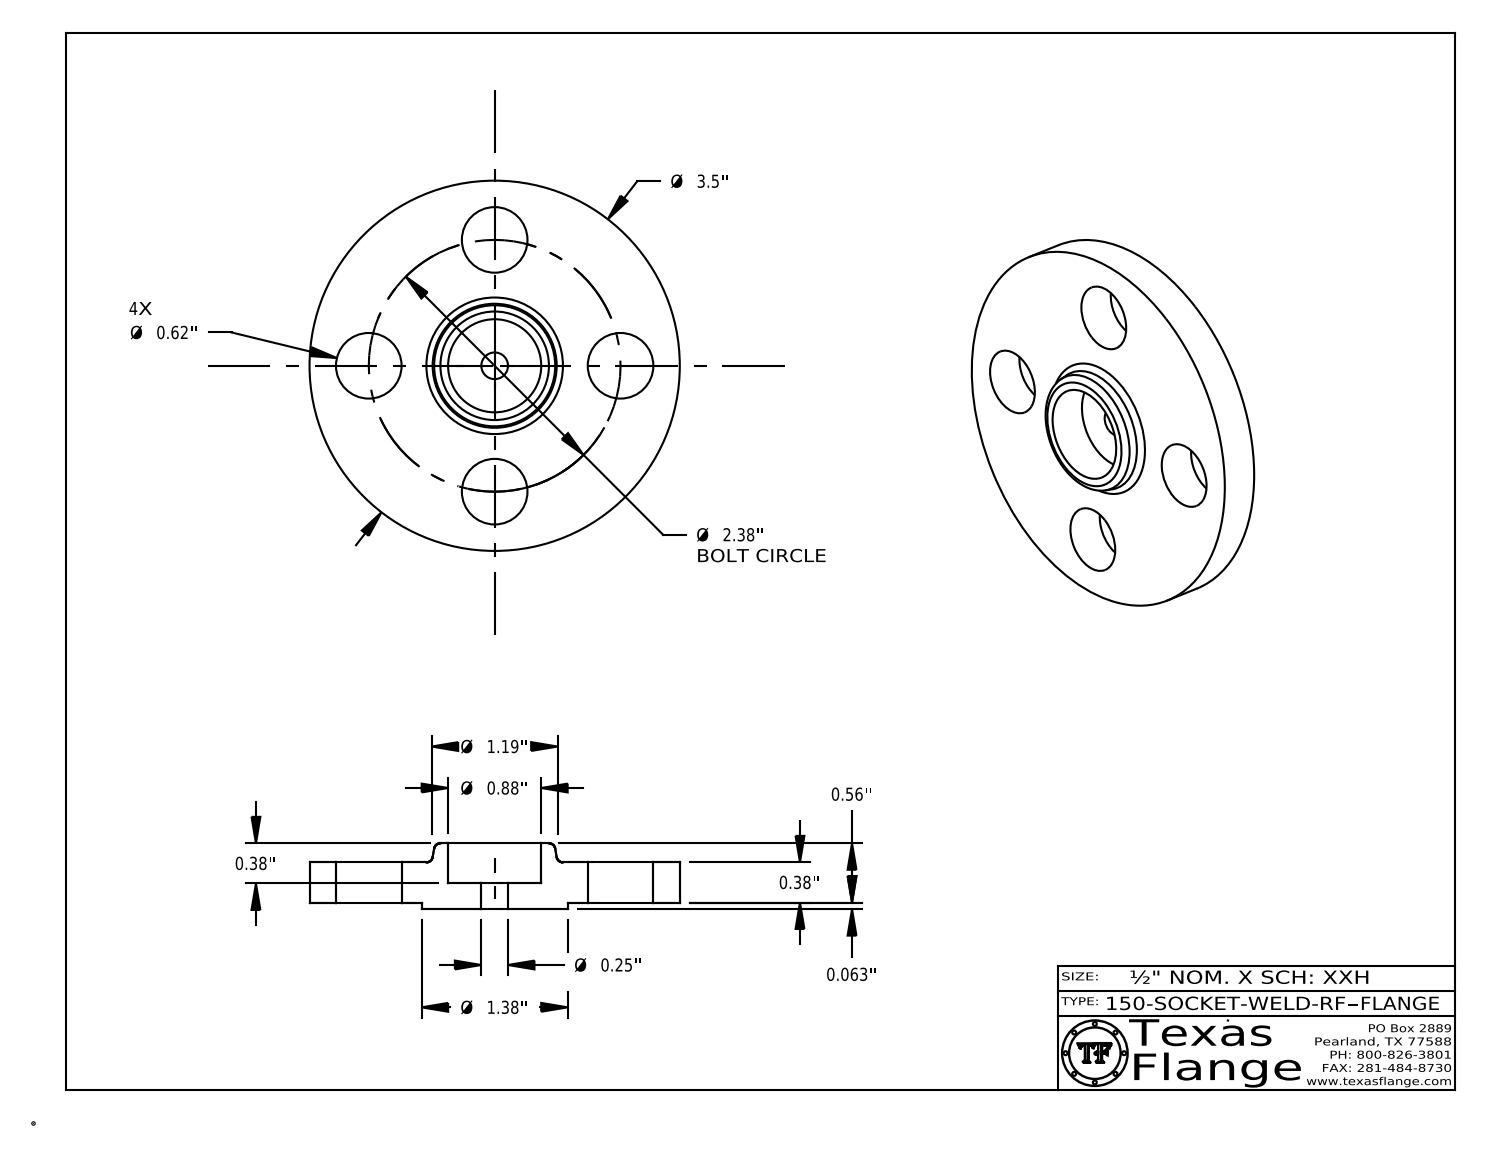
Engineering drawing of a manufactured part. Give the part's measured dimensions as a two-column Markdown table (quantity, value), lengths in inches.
| quantity | value |
| --- | --- |
| part name | 150-SOCKET-WELD-RF |
| STEP written by | CATIA V5 STEP AP214 (AUTOMOTIVE_DESIGN) |
| units | inches |
| bodies | 1 solid, 412 faces (370 planar, 36 cylindrical, 6 other) |
| overall size | 3.5 × 3.5 × 0.623 |
| volume | 3.236 in³ |
| surface area | 25.9 in² |
| round holes (diameter × count) | 0.62 × 4, 0.252 × 1, 0.495 × 1, 0.88 × 1 |
| round bosses / shafts (diameter × count) | 0.03 × 8, 3.5 × 1, 1.38 × 1, 0.39 × 1 |
| main face-to-face distances | 0.38, 0.063, 0.443, 0.18, 0.243, 0.2, 0.622, 0.56, 0.428, 0.365 |
| hole center spacings | 1.19, 1.683, 0.911, 2.199, 2.38, 1.19 |
